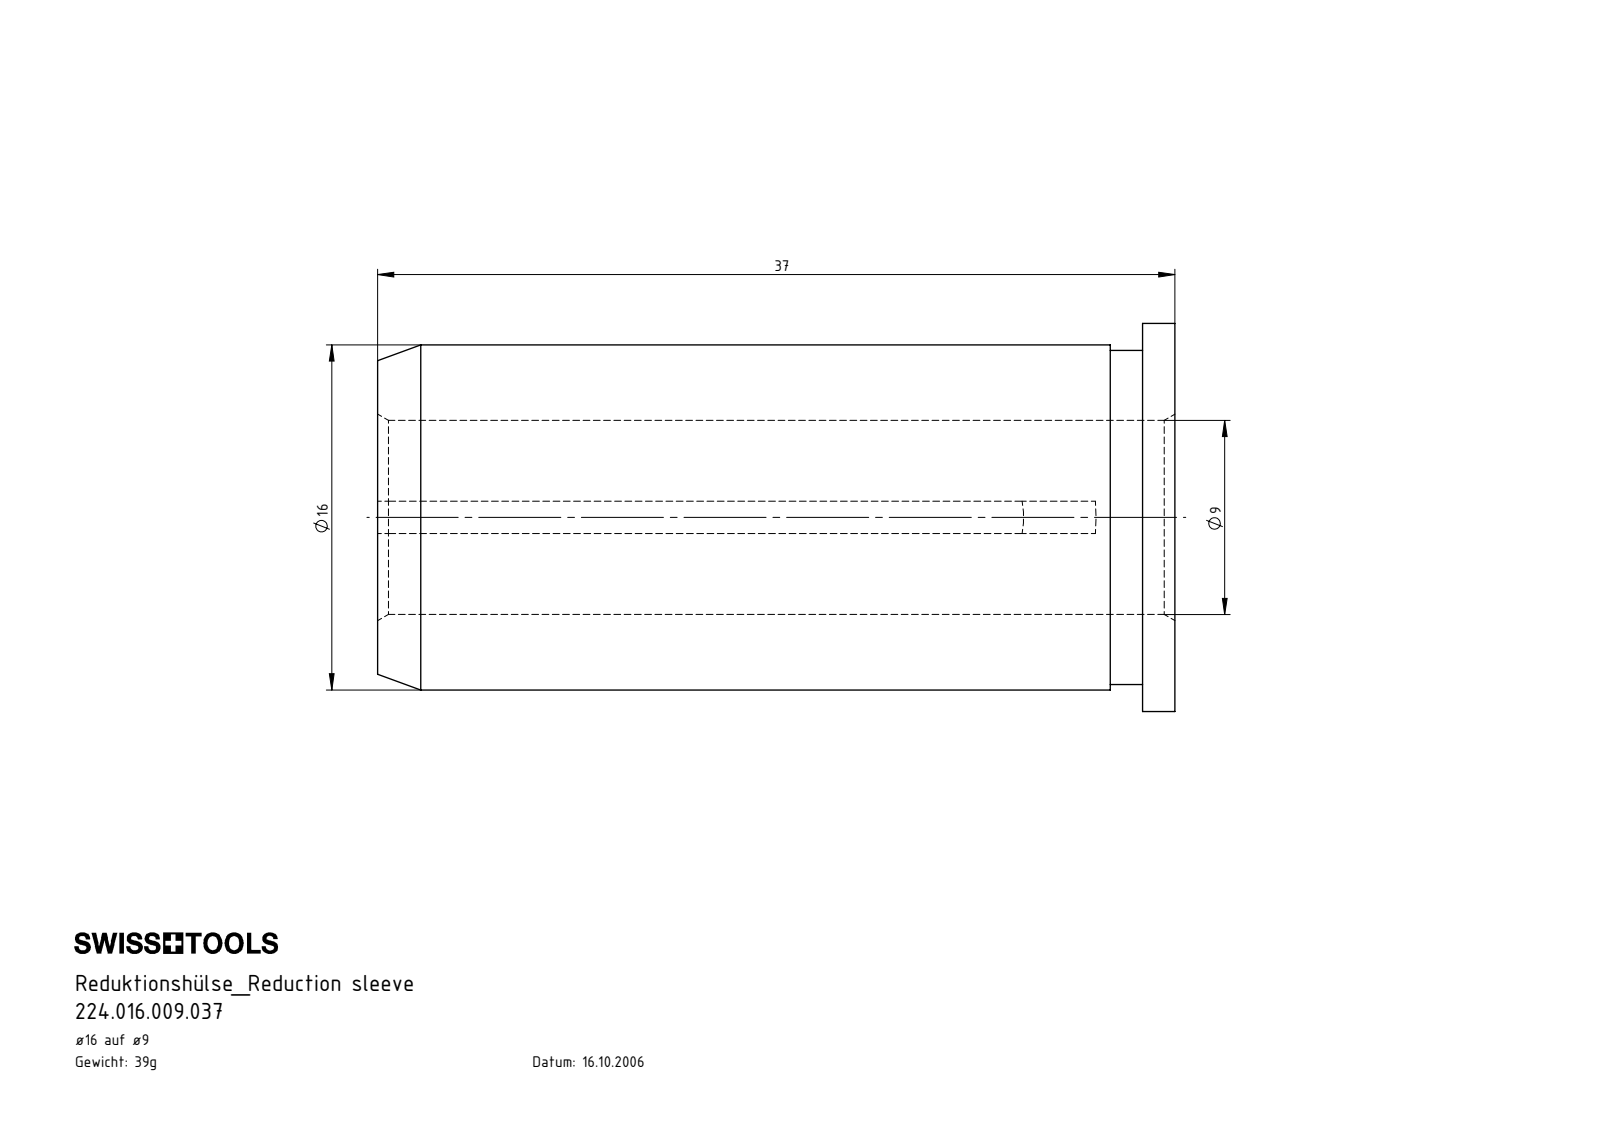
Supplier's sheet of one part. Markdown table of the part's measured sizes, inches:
| quantity | value |
| --- | --- |
| part name | U09.U16.001.037 |
| STEP written by | SolidWorks 2017 (AUTOMOTIVE_DESIGN) |
| units | inches |
| bodies | 1 solid, 14 faces (6 planar, 5 cylindrical, 3 other) |
| overall size | 1.457 × 0.709 × 0.709 |
| volume | 0.302 in³ |
| surface area | 5.278 in² |
| round holes (diameter × count) | 0.354 × 1 |
| round bosses / shafts (diameter × count) | 0.709 × 1, 0.63 × 1, 0.61 × 1 |
| partial cylindrical surfaces (radius × count) | 1.24 × 1 |
| main face-to-face distances | 0.059, 1.457, 1.398, 1.339, 0.118 |
